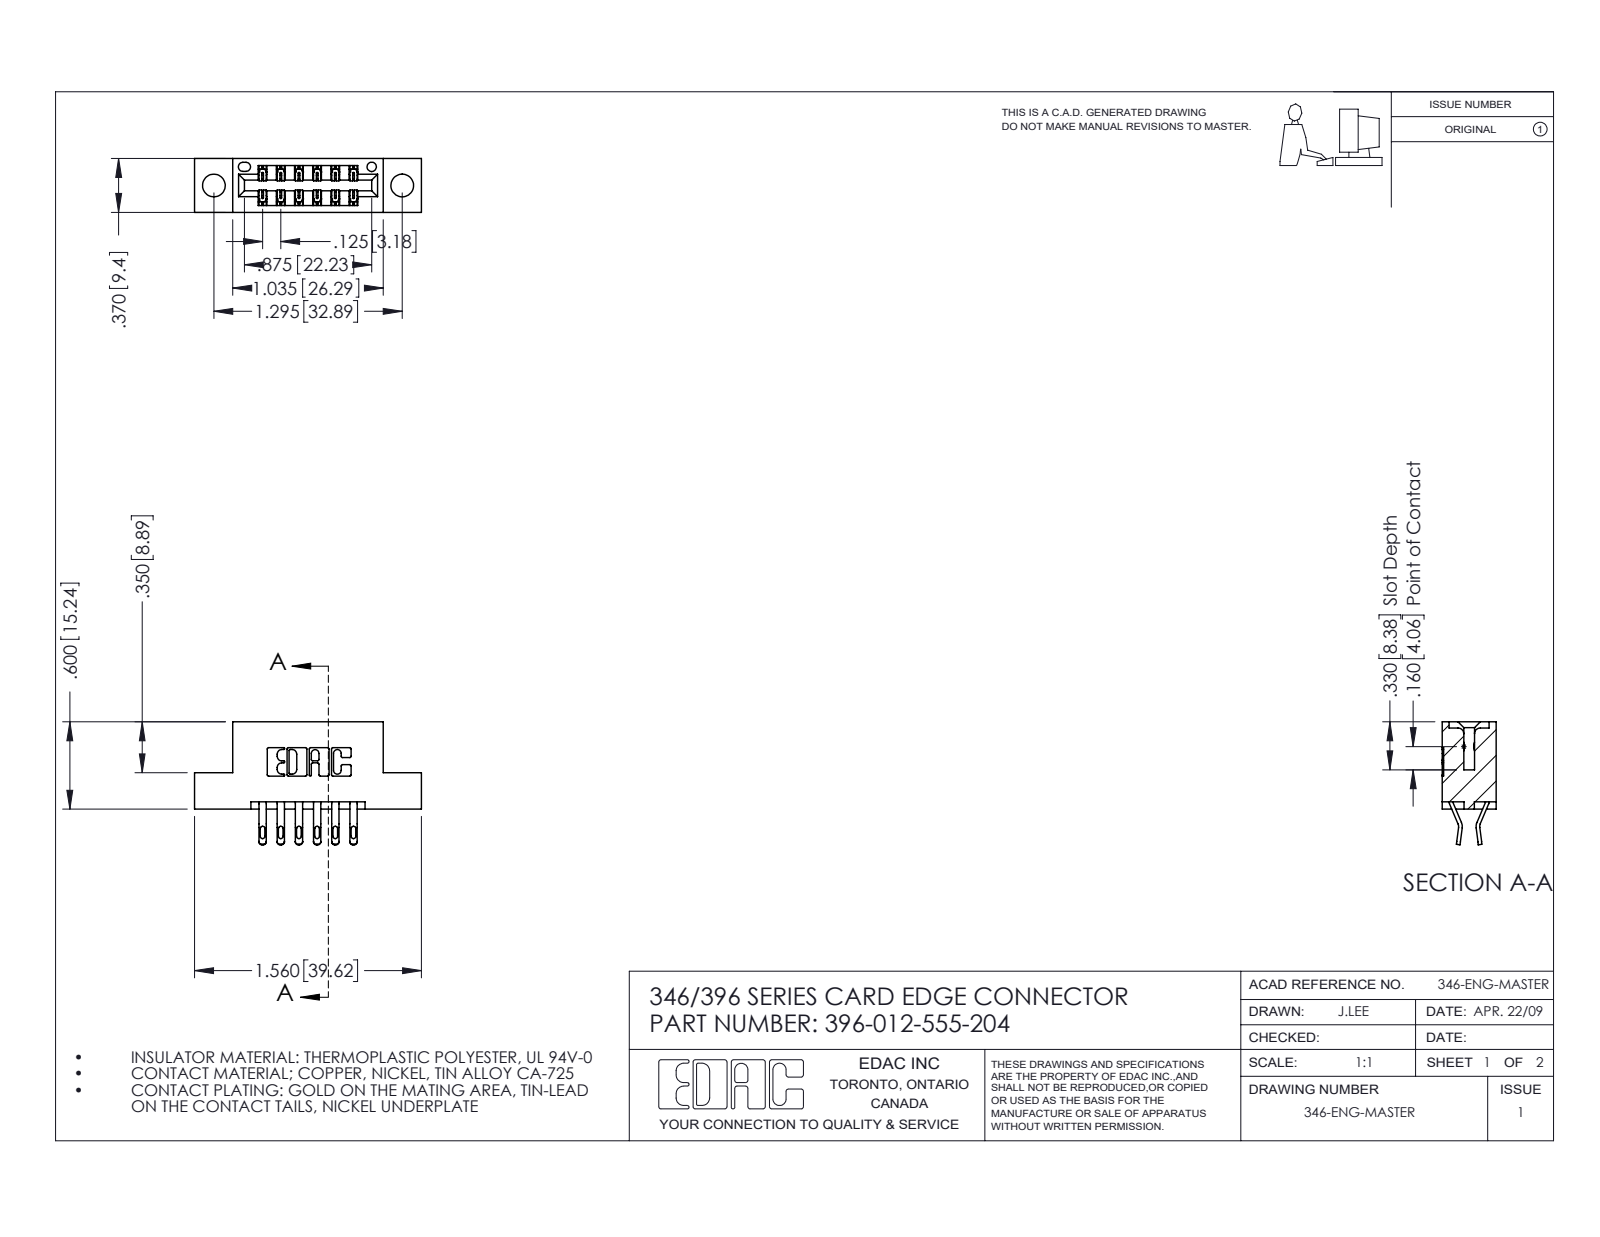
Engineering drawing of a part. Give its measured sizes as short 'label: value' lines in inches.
name: 396-012-555-204; 346 Part_Flush Mounting Lugs - 0.156 Dia-TH; 345-292-001_555 Tail
written by: SolidWorks 2016 (CONFIG_CONTROL_DESIGN)
unit: in
bodies: 13 solids, 818 faces (472 planar, 346 cylindrical, 0 other)
size: 1.56 × 0.845 × 0.37
volume: 0.215 in³; area: 6.549 in²
holes: 2× ⌀0.156, 1× ⌀0.064
rounds: 24× R0.016, 24× R0.02, 22× R0.01, 18× R0.006, 6× R0.007, 6× R0.031, 3× R0.026, 2× R0.01
face distances: 0.25, 0.37, 0.048, 0.322, 0.125, 0.148, 0.222, 0.1, 0.174, 0.025
hole spacings: 0.246, 1.092, 1.295
